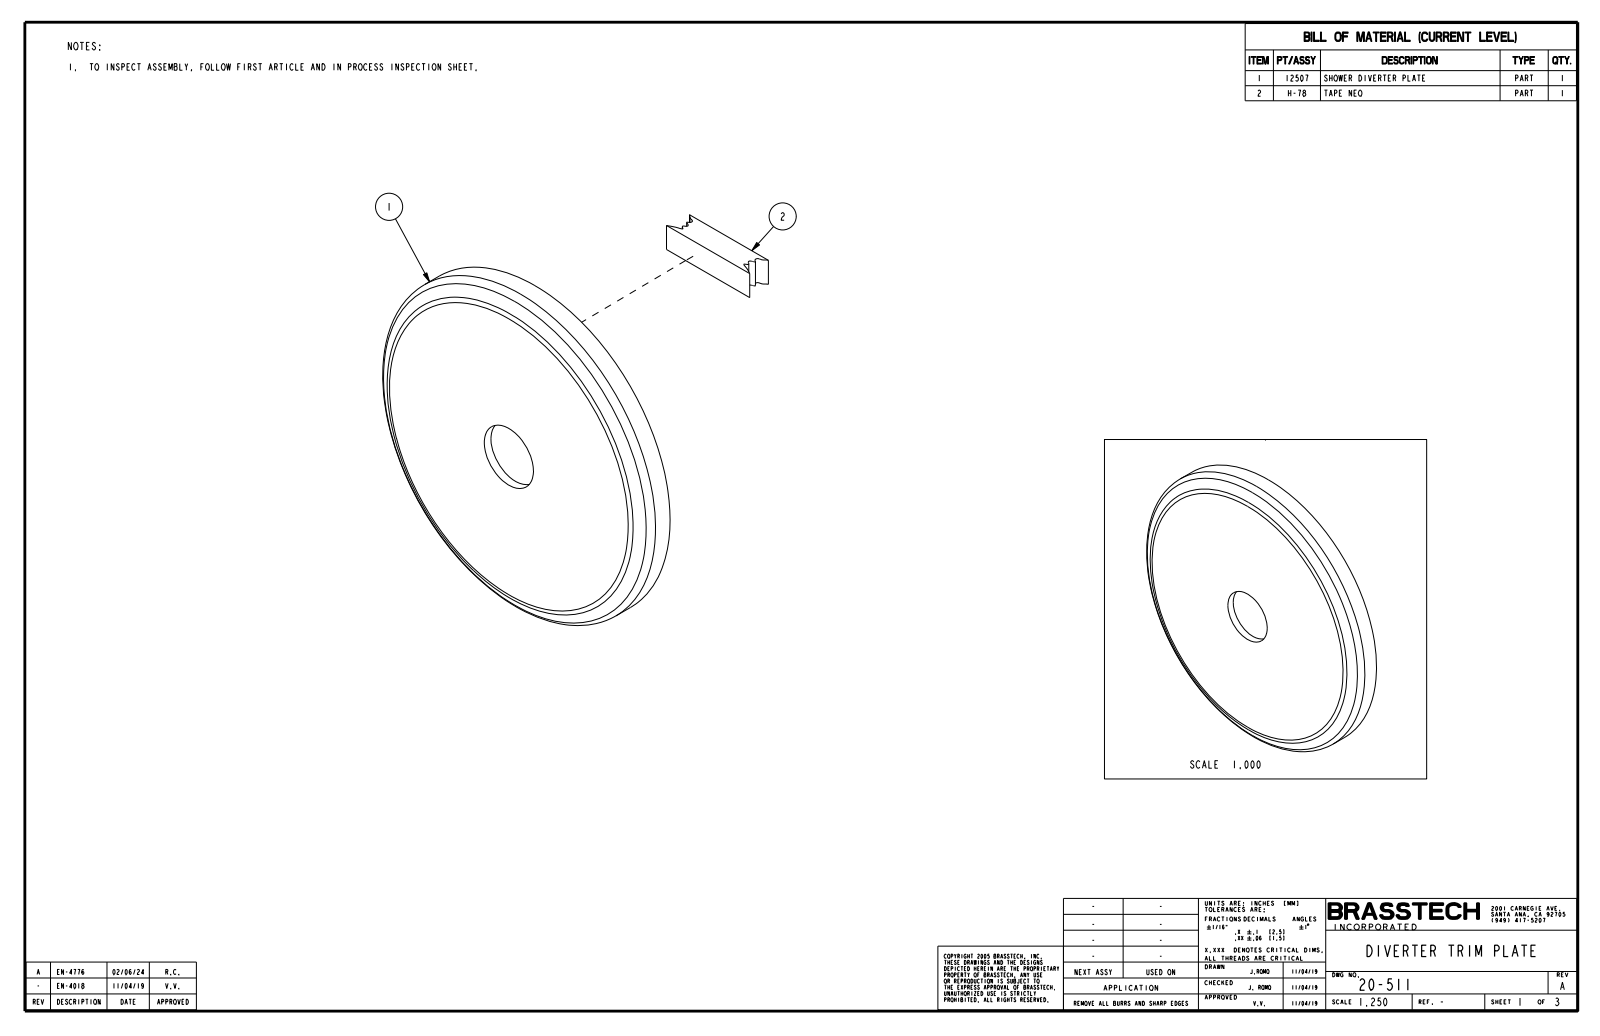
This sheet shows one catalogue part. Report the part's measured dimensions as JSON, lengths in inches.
{"part_name": "12507; 20-511_ASM", "step_written_by": "CREO PARAMETRIC BY PTC INC, 2023134 (CONFIG_CONTROL_DESIGN)", "units": "inches", "bodies": {"solids": 1, "faces": 22, "planar": 4, "cylindrical": 8, "other": 10}, "overall_size": [3.25, 3.25, 0.313], "volume_in3": 0.833, "surface_area_in2": 20.65, "round_holes": [[0.59, 1], [2.59, 1], [3.09, 1]], "round_bosses_or_shafts": [[3.25, 1]], "face_to_face_distances": [0.08, 0.043, 0.122, 0.19, 0.233, 0.313]}
